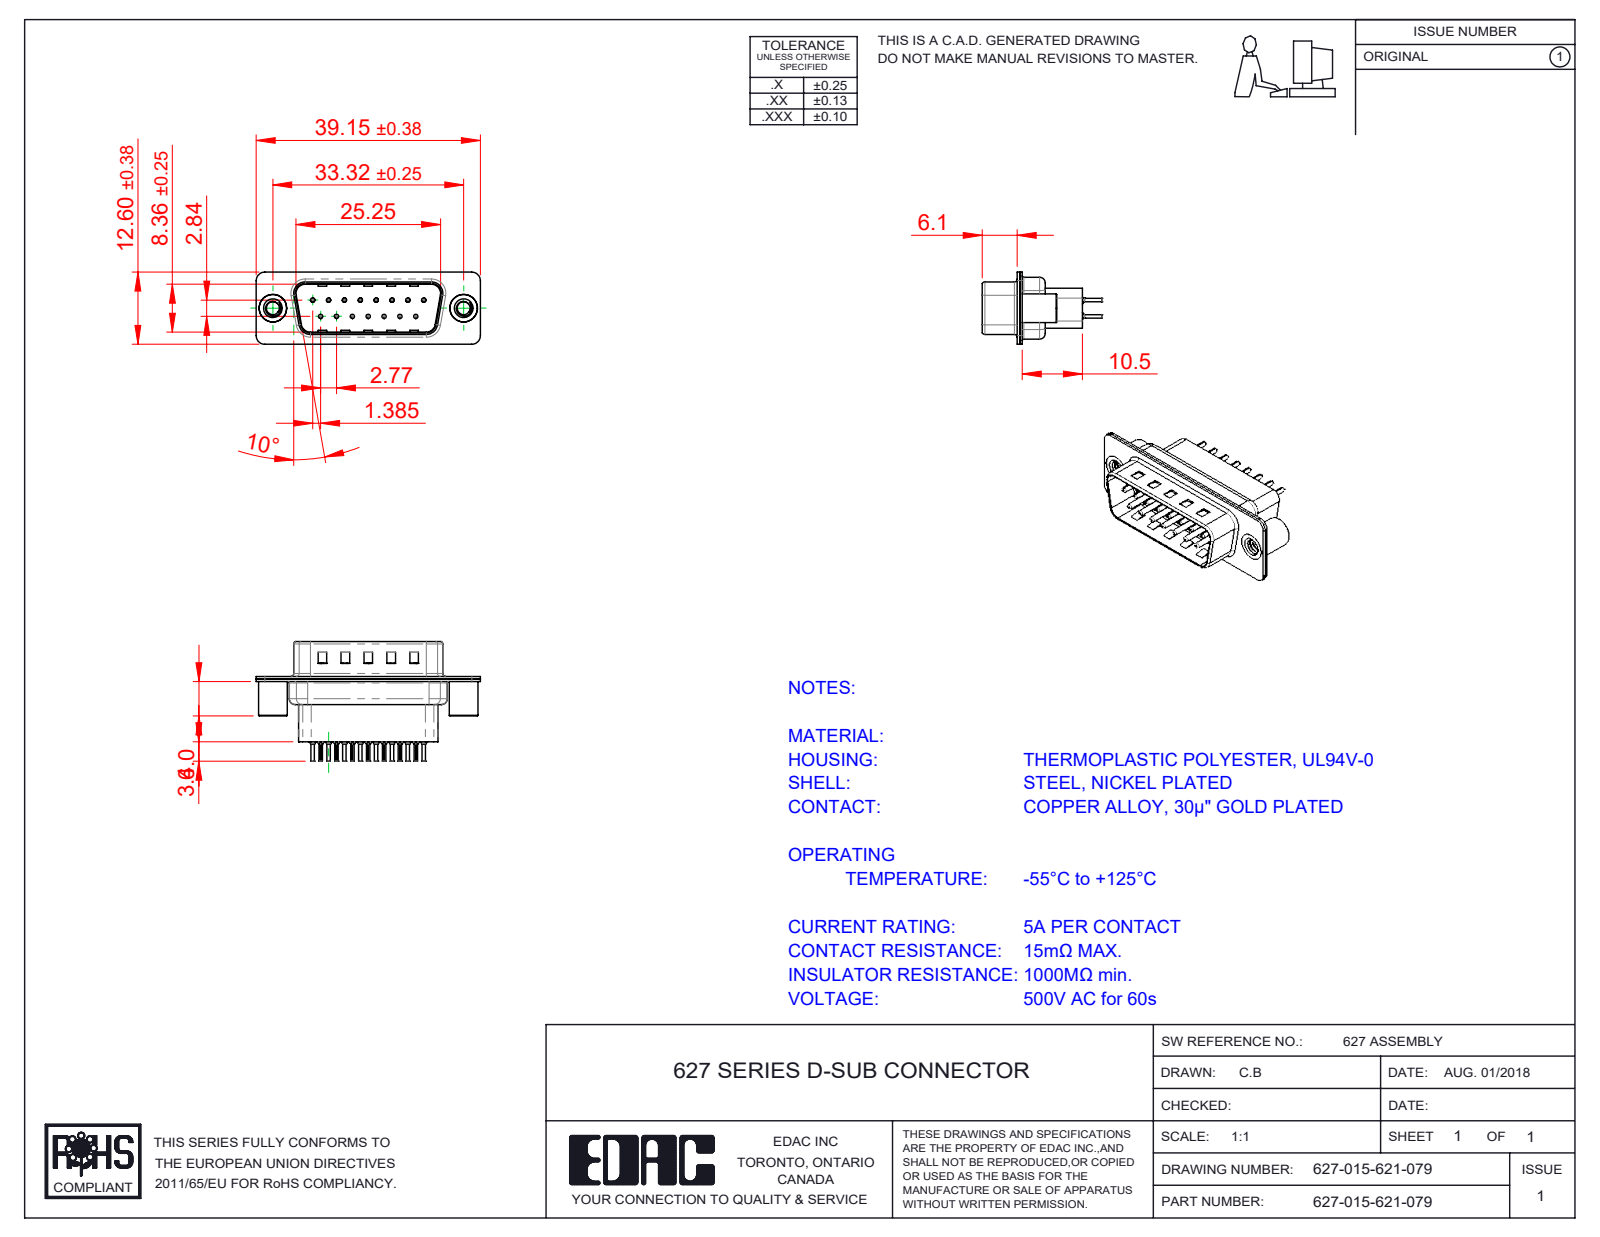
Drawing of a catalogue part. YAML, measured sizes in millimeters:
part_name: "627 Contact Row 2_21H; 627 Shell Front_15 Contacts; 627 4-40 Threaded Standoff BS; 627-015-621-079 (+3 more)"
step_written_by: "SolidWorks 2020 (CONFIG_CONTROL_DESIGN)"
units: millimeters
bodies: {solids: 20, faces: 1832, planar: 499, cylindrical: 708, other: 625}
overall_size: [39.15, 20.8, 12.6]
volume: 2635
surface_area: 6801
round_holes:
  - {diameter: 0.2, count: 15}
  - {diameter: 0.35, count: 15}
  - {diameter: 1.1, count: 15}
  - {diameter: 1.6, count: 15}
  - {diameter: 2.26, count: 2}
  - {diameter: 4, count: 2}
  - {diameter: 4.8, count: 2}
round_bosses_or_shafts:
  - {diameter: 2, count: 15}
  - {diameter: 1.5, count: 15}
  - {diameter: 0.75, count: 15}
  - {diameter: 0.6, count: 15}
  - {diameter: 5, count: 2}
  - {diameter: 4.9, count: 2}
partial_cylinders:
  - {radius: 0.1, count: 30}
  - {radius: 1.5, count: 16}
  - {radius: 2, count: 12}
  - {radius: 0.5, count: 8}
  - {radius: 1.6, count: 8}
  - {radius: 0.25, count: 4}
  - {radius: 0.6, count: 4}
  - {radius: 0.65, count: 4}
face_to_face_distances: [0.4, 0.45, 0.9, 0.82, 9.58, 1.5, 0.68, 7.68, 1.4, 1.08]
hole_center_spacings: [3.16, 2.77, 5.54, 8.31, 11.08, 5.03, 5.04, 7.48]
